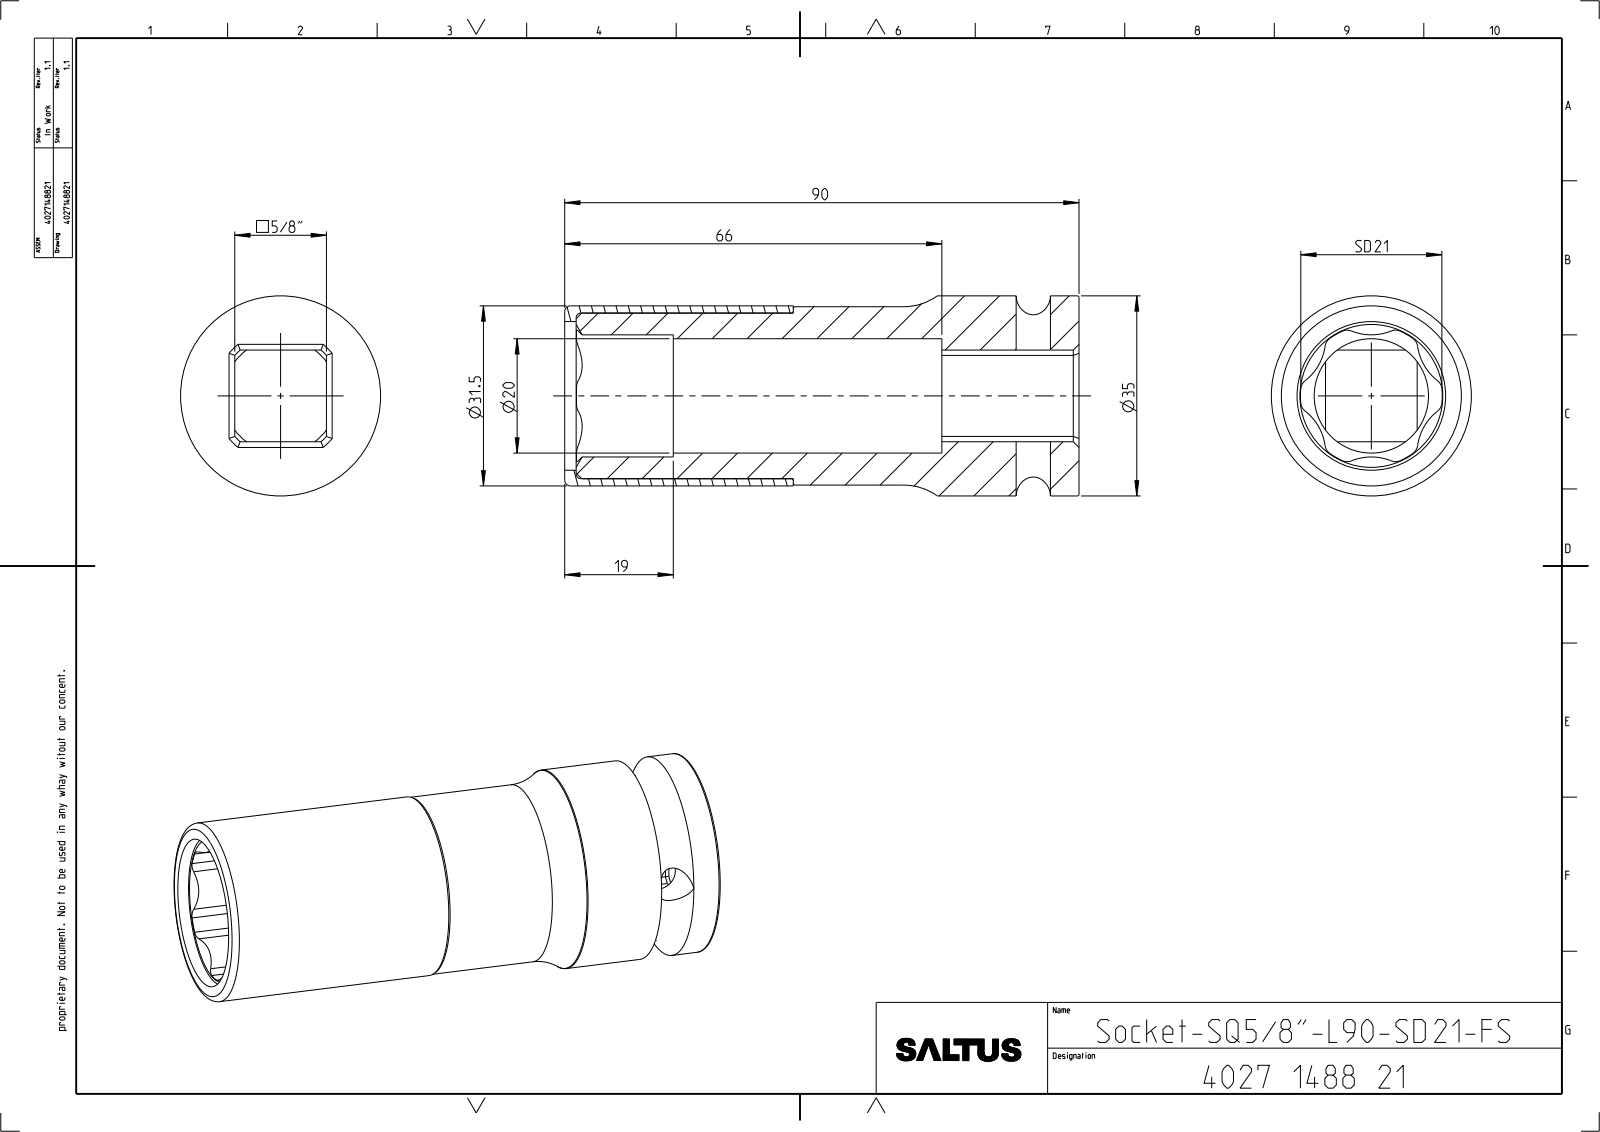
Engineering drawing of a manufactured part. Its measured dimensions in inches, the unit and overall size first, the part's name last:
Units: inches
Overall size (bounding box): 3.543 × 1.378 × 1.378
Round holes (diameter × count): ⌀0.236 ×1, ⌀0.787 ×1, ⌀1.024 ×1, ⌀1.14 ×1
Round bosses / shafts (diameter × count): ⌀1.378 ×1, ⌀1.24 ×1, ⌀1.228 ×1, ⌀1.142 ×1
Partial cylindrical surfaces — rounded edges, fillets, slot ends (radius × count): R0.079 ×12, R0.366 ×6, R0.421 ×1, R0.489 ×1
Main face-to-face distances: 0.631, 1.969, 3.543, 1.575, 3.465, 1.496, 0.079, 2.795, 0.827, 0.669
Volume: 2.663 in³ · Surface area: 37.15 in²
Bodies: 2 solids, 95 faces (23 planar, 48 cylindrical, 24 other)
Part name (STEP PRODUCT): 4027911134; 4027299505; 4027148821_ASM
STEP written by: CREO PARAMETRIC BY PTC INC, 2022414 (CONFIG_CONTROL_DESIGN)
